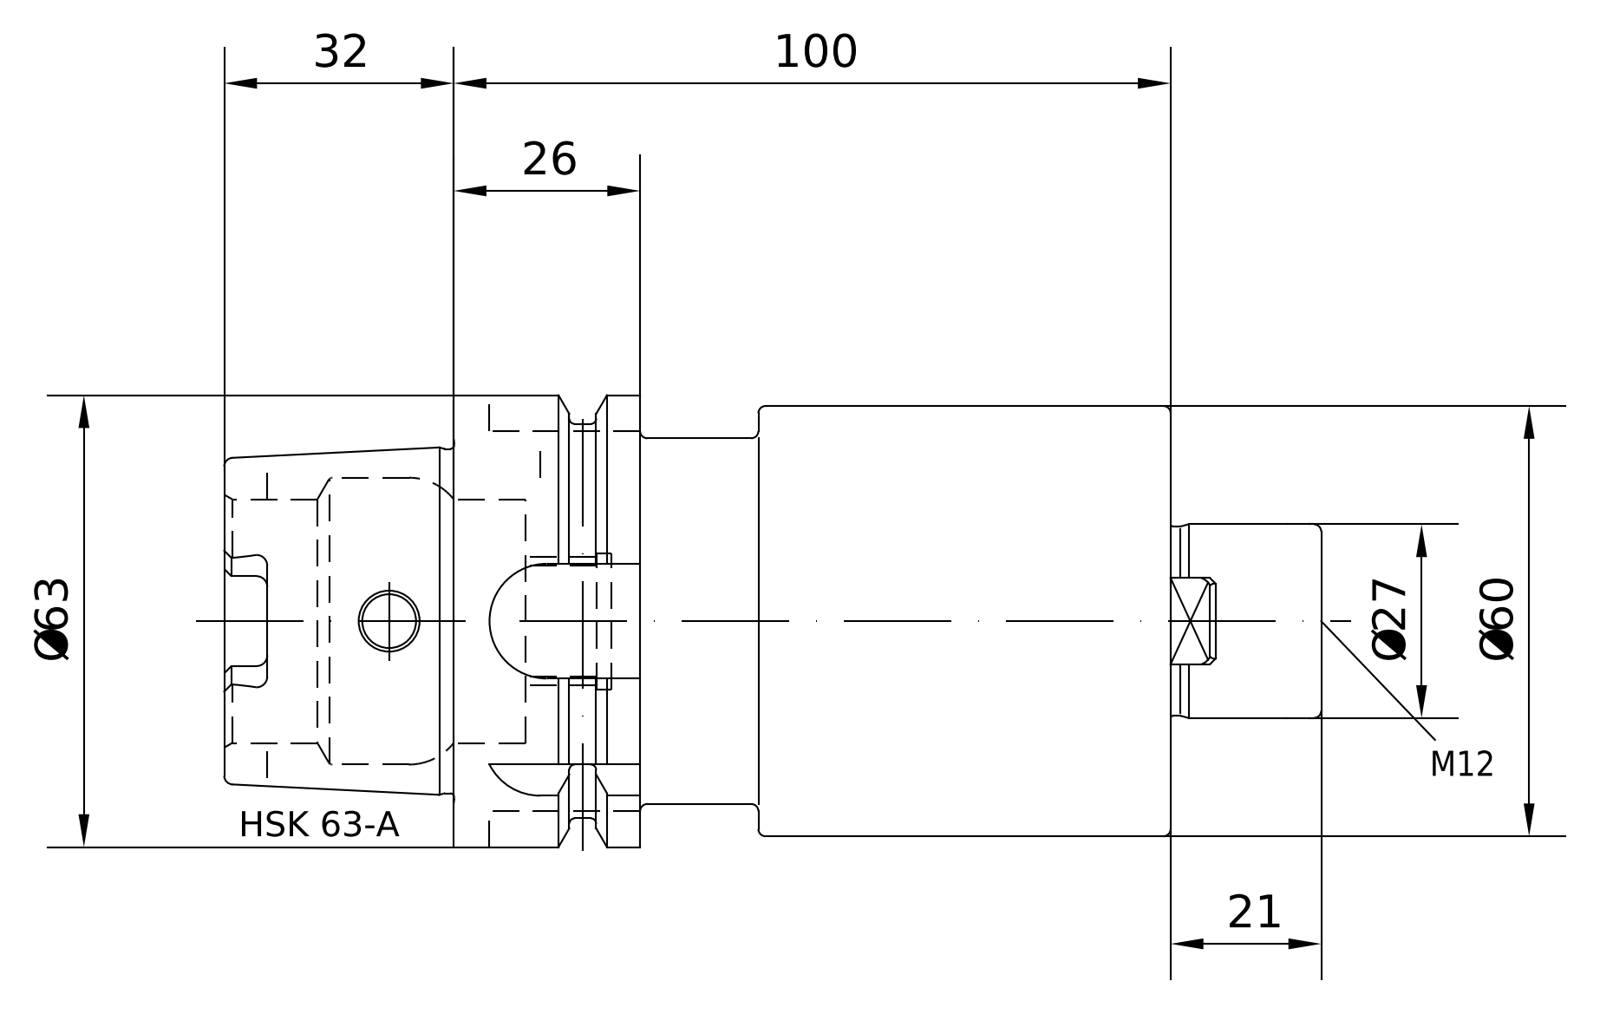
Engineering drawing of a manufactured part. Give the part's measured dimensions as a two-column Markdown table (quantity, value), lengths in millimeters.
| quantity | value |
| --- | --- |
| part name | A63-051-27 |
| STEP written by | PRO/ENGINEER BY PARAMETRIC TECHNOLOGY CORPORATION, 2010430 (CONFIG_CONTROL_DESIGN) |
| units | millimeters |
| bodies | 1 solid, 198 faces (70 planar, 54 cylindrical, 74 other) |
| overall size | 153 × 63 × 63 |
| volume | 288 944 mm³ |
| surface area | 41 789 mm² |
| round holes (diameter × count) | 7.5 × 1, 10 × 1, 10.2 × 1, 12 × 1, 16.92 × 1, 18.32 × 1, 18.66 × 1, 34 × 1, 40 × 1 |
| round bosses / shafts (diameter × count) | 63 × 1, 60 × 1, 55 × 1, 51 × 1, 48.04 × 1, 27 × 1, 18 × 1 |
| partial cylindrical surfaces (radius × count) | 1.5 × 6, 3 × 4, 8 × 1, 8.02 × 1, 9.02 × 1 |
| main face-to-face distances | 100, 26, 74, 10, 16, 90, 121, 95, 42, 42.5 |
